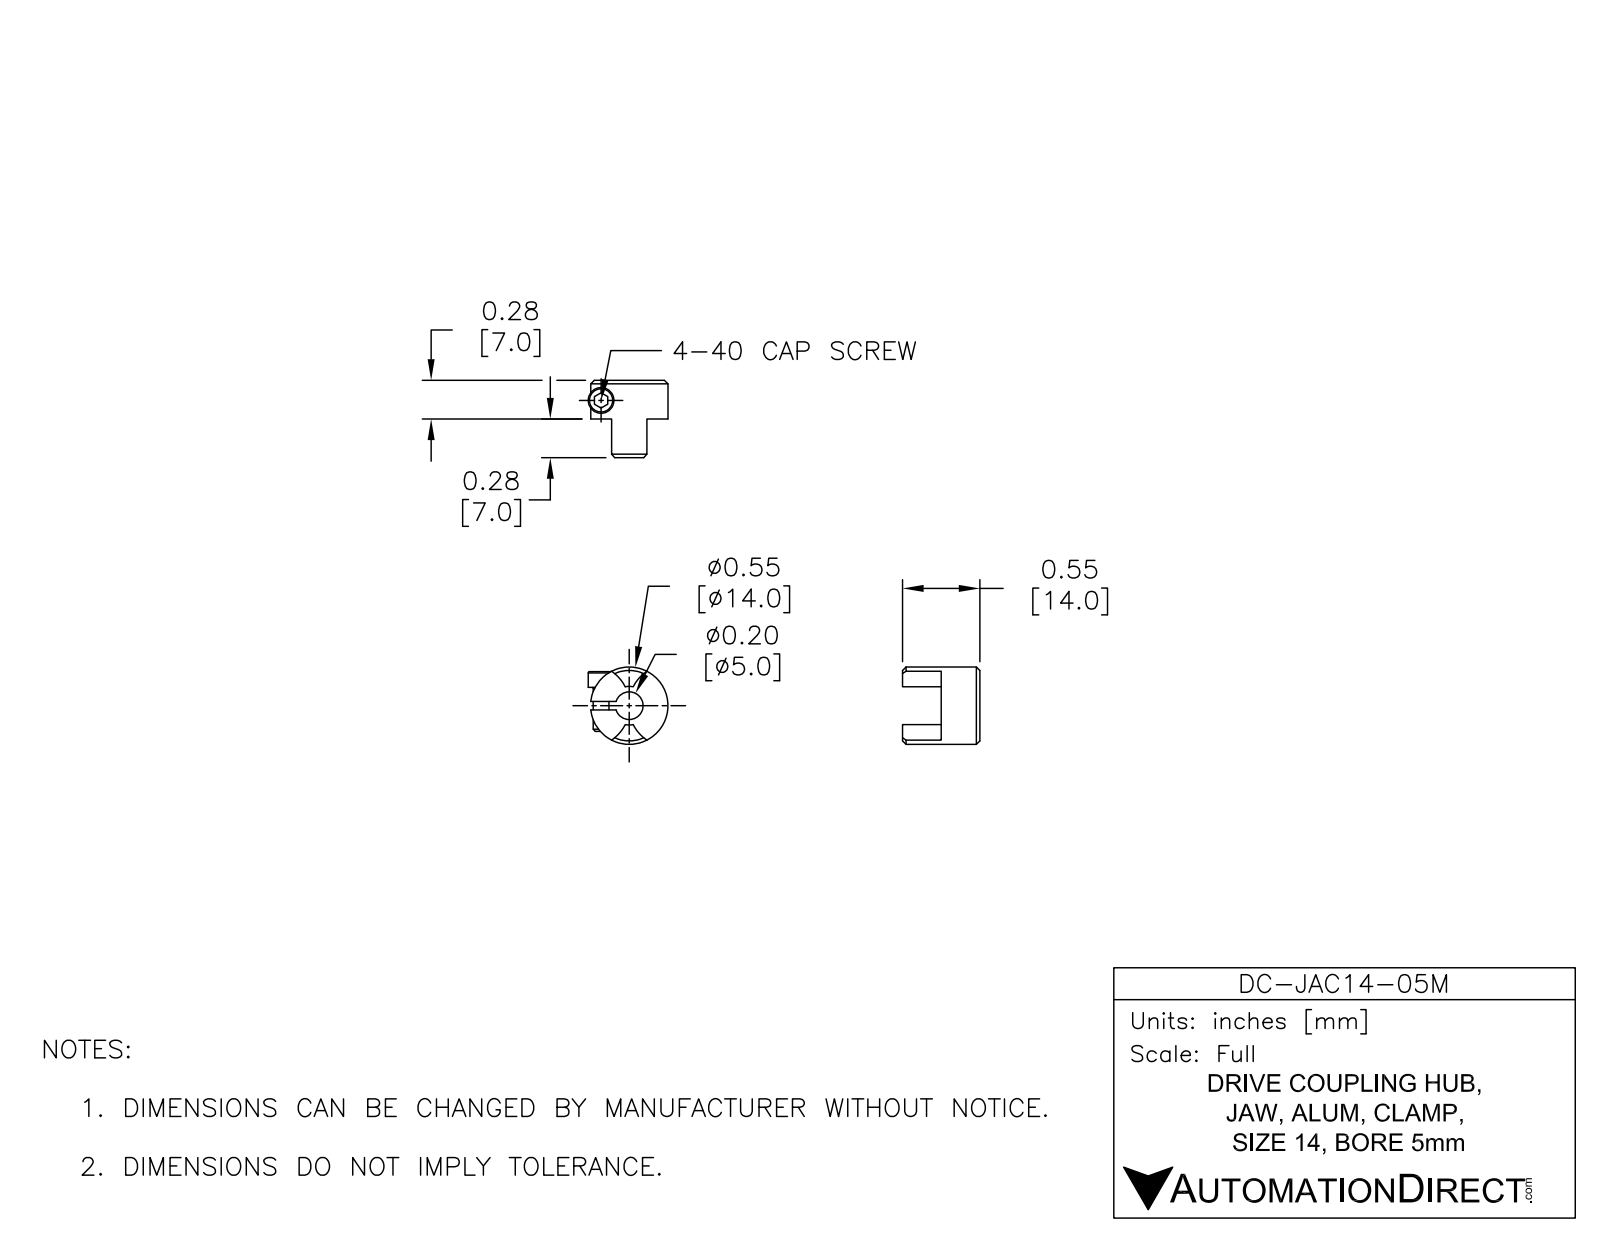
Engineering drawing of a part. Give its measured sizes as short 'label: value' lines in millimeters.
name: DC-JAC14-05M
written by: SolidWorks 2015 (AUTOMOTIVE_DESIGN)
unit: mm
bodies: 1 solid, 30 faces (7 planar, 17 cylindrical, 6 other)
size: 13.97 × 13.97 × 13.93
volume: 978 mm³; area: 944 mm²
holes: 1× ⌀3.28, 1× ⌀5
bosses: 1× ⌀13.97
rounds: 2× R7.52, 1× R2.39, 1× R3.49
face distances: 6.99, 1.52, 13.97, 6.98, 2.54, 4.06
